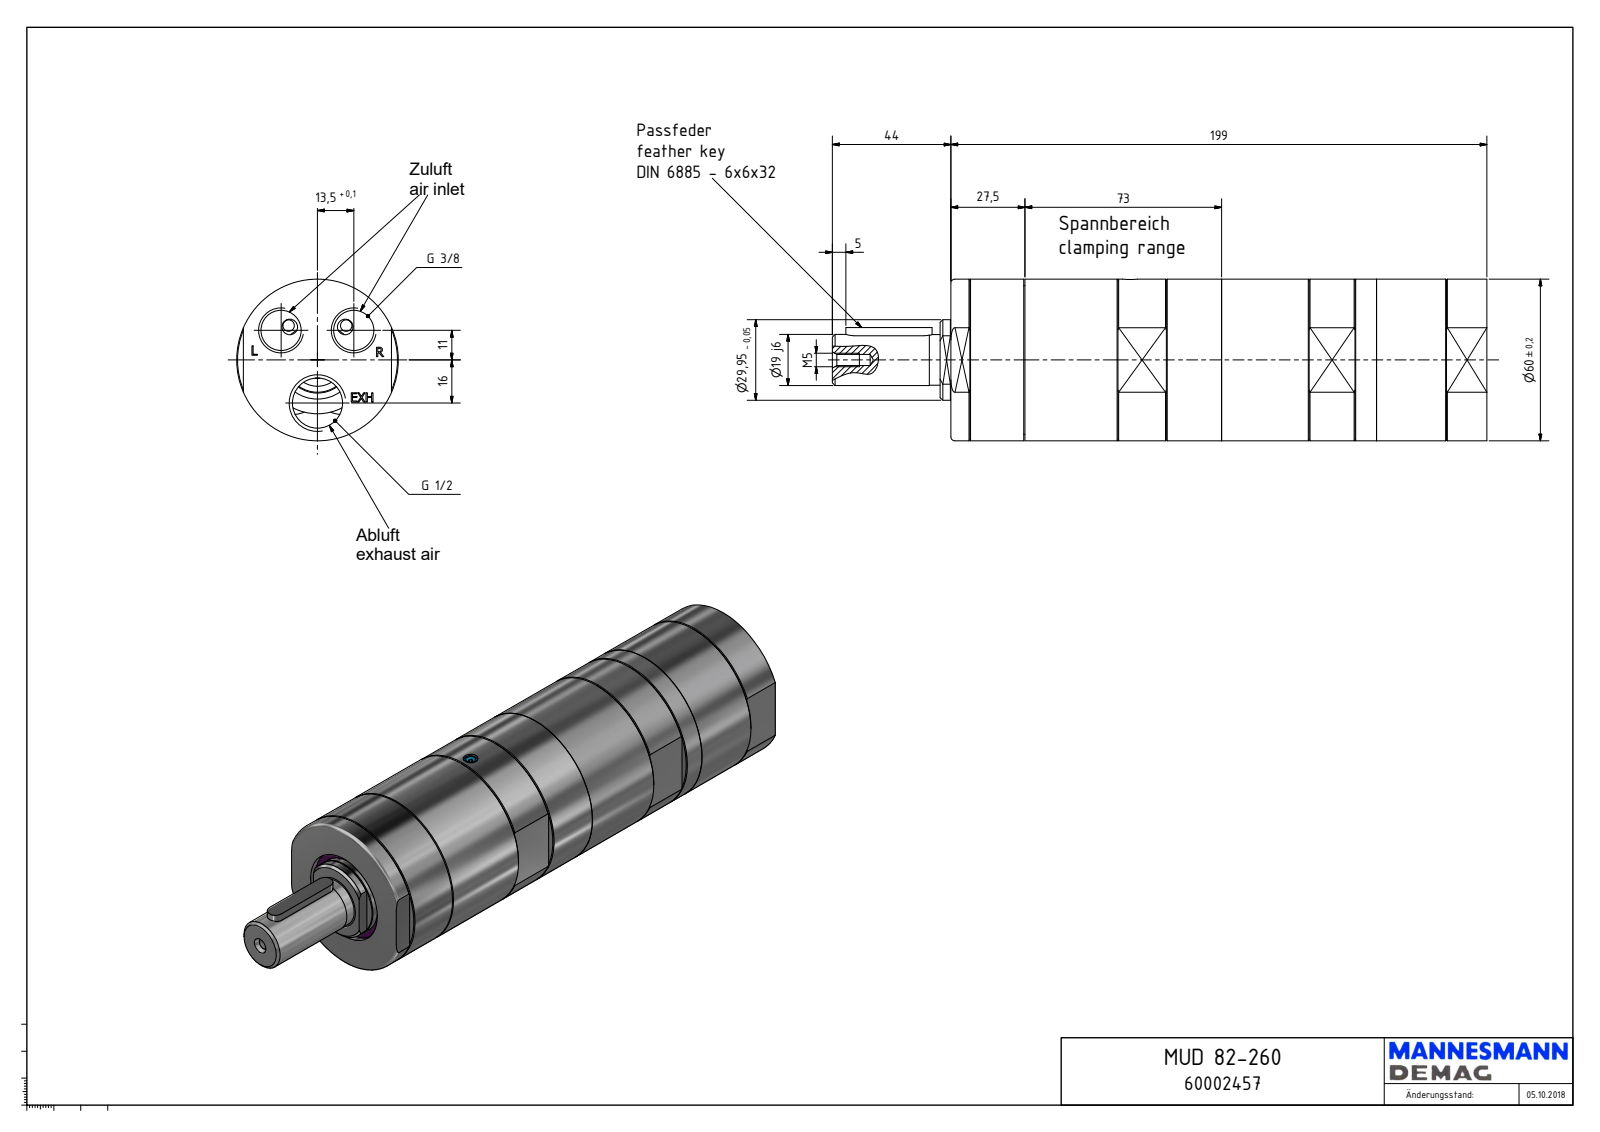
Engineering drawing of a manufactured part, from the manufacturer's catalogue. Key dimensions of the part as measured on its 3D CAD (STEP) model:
Part name (STEP PRODUCT): Bauteil4
STEP written by: Autodesk Inventor 2018 (AUTOMOTIVE_DESIGN)
Units: millimetres
Bodies: 1 solid, 200 faces (109 planar, 46 cylindrical, 45 other)
Overall size (bounding box): 243 × 60 × 60
Volume: 557 338 mm³ · Surface area: 52 954 mm²
Round holes (diameter × count): ⌀14.95 ×2, ⌀1.55 ×1, ⌀4 ×1, ⌀4.13 ×1, ⌀5.5 ×1, ⌀18.63 ×1, ⌀35 ×1, ⌀55.38 ×1
Round bosses / shafts (diameter × count): ⌀60 ×1, ⌀55.18 ×1, ⌀29.95 ×1, ⌀19 ×1, ⌀18.8 ×1, ⌀5 ×1, ⌀3.6 ×1
Partial cylindrical surfaces — rounded edges, fillets, slot ends (radius × count): R3 ×2, R7.5 ×2, R8.5 ×1, R19.07 ×1, R23.5 ×1, R25.02 ×1, R29.02 ×1
Main face-to-face distances: 199, 55, 16.09, 182.91, 3.09, 186, 13, 27.5, 155.41, 158.5
Hole centre spacings: 17.41, 30.19, 16, 27
